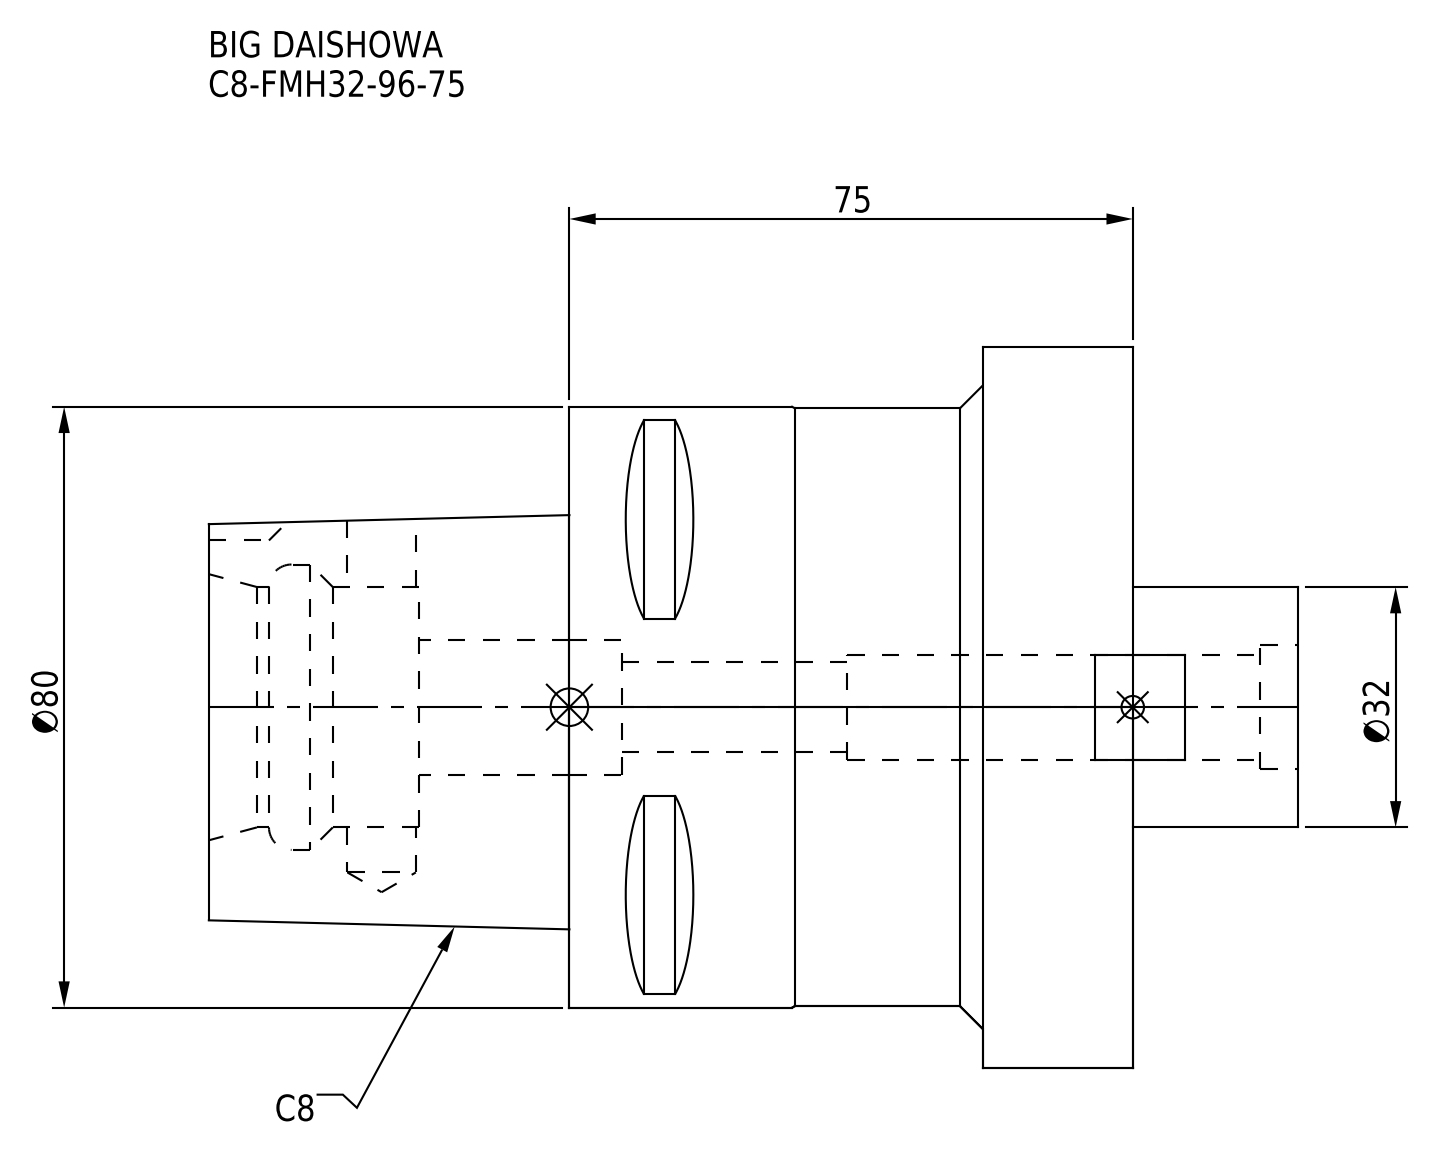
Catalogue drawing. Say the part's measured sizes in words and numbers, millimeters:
The part is named "C8-FMH32-96-75". Its 3-D file was written by "CREO PARAMETRIC BY PTC INC, 2016380 (AUTOMOTIVE_DESIGN)". It is 1 solid with 82 faces: 41 planar, 27 cylindrical and 14 other. Overall it measures 145 by 96 by 96 millimeters. Its volume is 504 248 cubic millimeters and its surface area 54 424 square millimeters. Round holes: 1 of diameter 9.1, 1 of diameter 12, 1 of diameter 14, 1 of diameter 16.5, 1 of diameter 18, 1 of diameter 32, 1 of diameter 38. Round bosses or shafts: 1 of diameter 96, 1 of diameter 80, 1 of diameter 79.6. Partial cylindrical surfaces (rounded edges, fillets, slot ends): 1 of radius 6. The main face-to-face distances are 75, 20, 55, 48, 123, 103, 7, 27, 82, 130.
